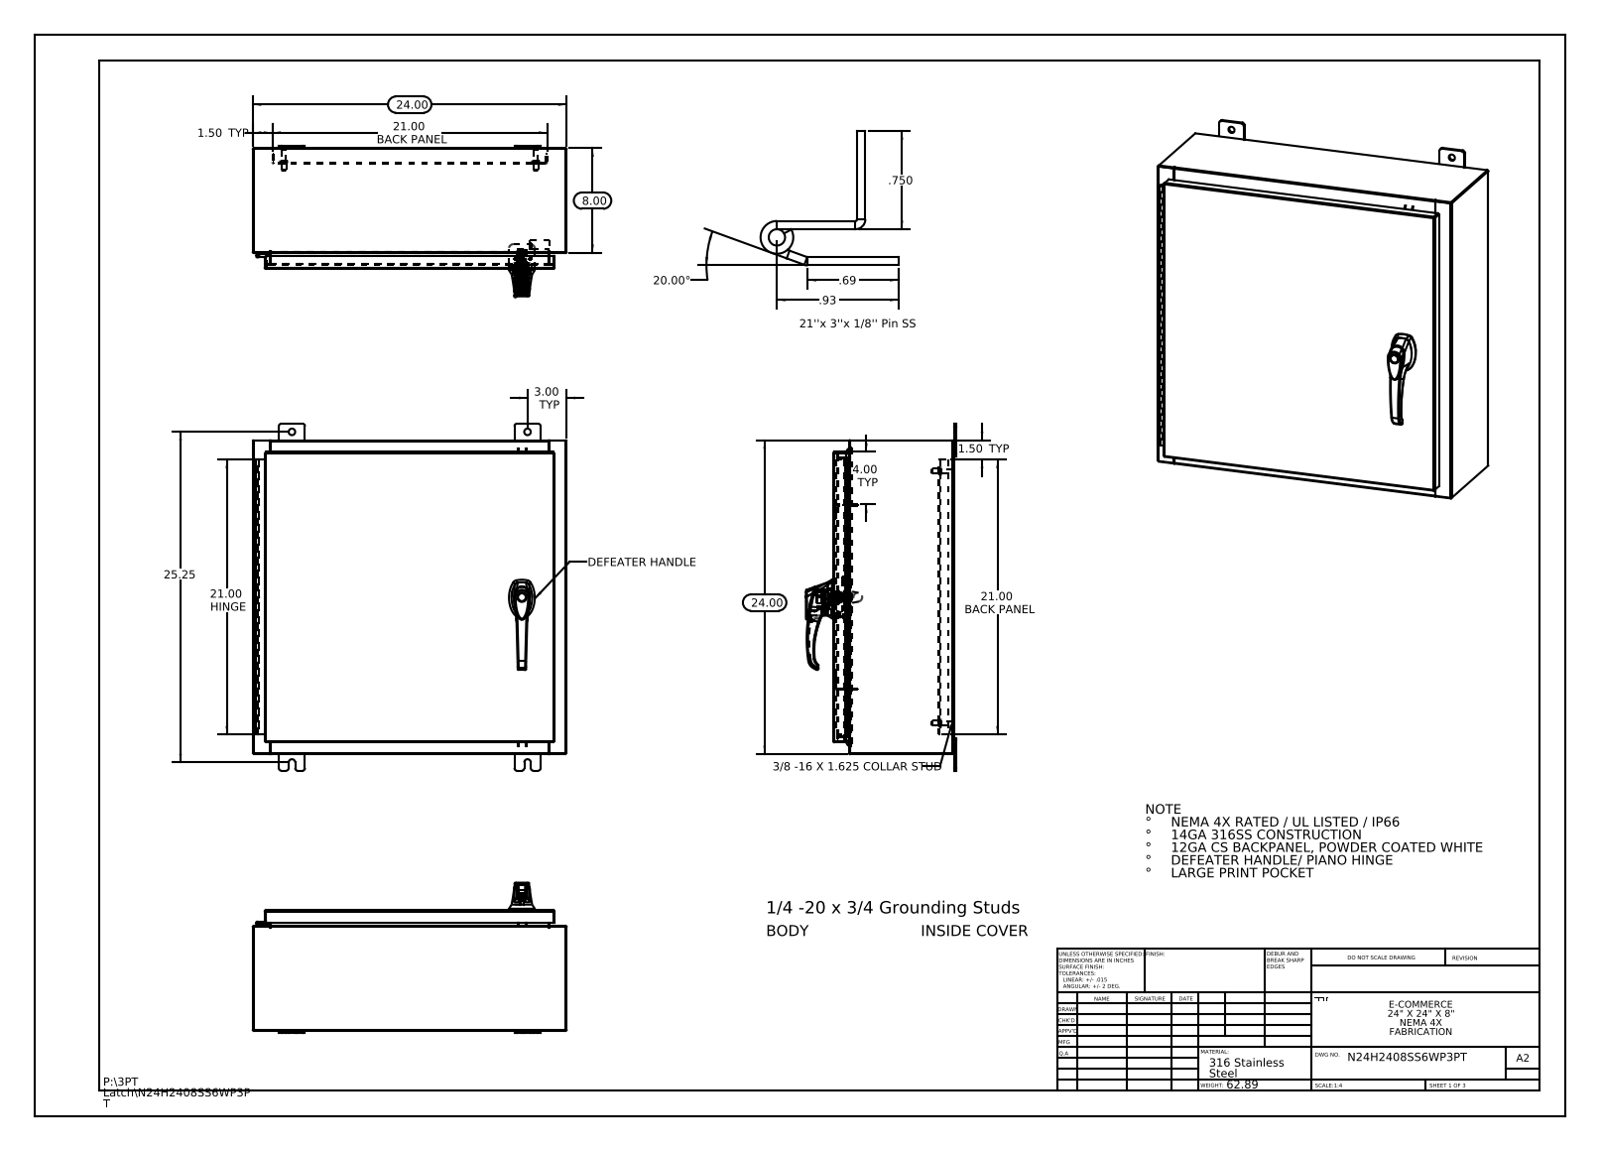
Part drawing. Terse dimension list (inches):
name: NMP-SS-RODGUIDES; N24H2408SS6WP3PT Defeater Handle Rod; N24H2408SS6WP3PT Cover; N24H2408SS6WP3PT Bottom (+8 more)
written by: SolidWorks 2013 (CONFIG_CONTROL_DESIGN)
unit: in
bodies: 31 solids, 2412 faces (865 planar, 893 cylindrical, 654 other)
size: 26.5 × 24 × 11.495
volume: 223.3 in³; area: 5 520 in²
holes: 8× ⌀0.5, 4× ⌀0.25, 3× ⌀0.138, 3× ⌀0.161, 2× ⌀0.079, 2× ⌀0.203, 2× ⌀0.313, 2× ⌀0.437, 1× ⌀0.125, 1× ⌀0.125, 1× ⌀0.197, 1× ⌀0.276
bosses: 4× ⌀0.625, 4× ⌀0.375, 4× ⌀0.33, 1× ⌀1.181, 1× ⌀0.748, 1× ⌀0.68, 1× ⌀0.661, 1× ⌀0.639
rounds: 37× R0.118, 33× R0.006, 24× R0.19, 22× R0.013, 18× R0.088, 15× R0.039, 12× R0.028, 6× R0.008
face distances: 0.075, 9.126, 23.925, 9.051, 9.201, 0.104, 1, 1.075, 8.051, 8.126
hole spacings: 7.68, 0.295, 0.625, 0.841, 1.25, 1.313, 1.561, 1.858
